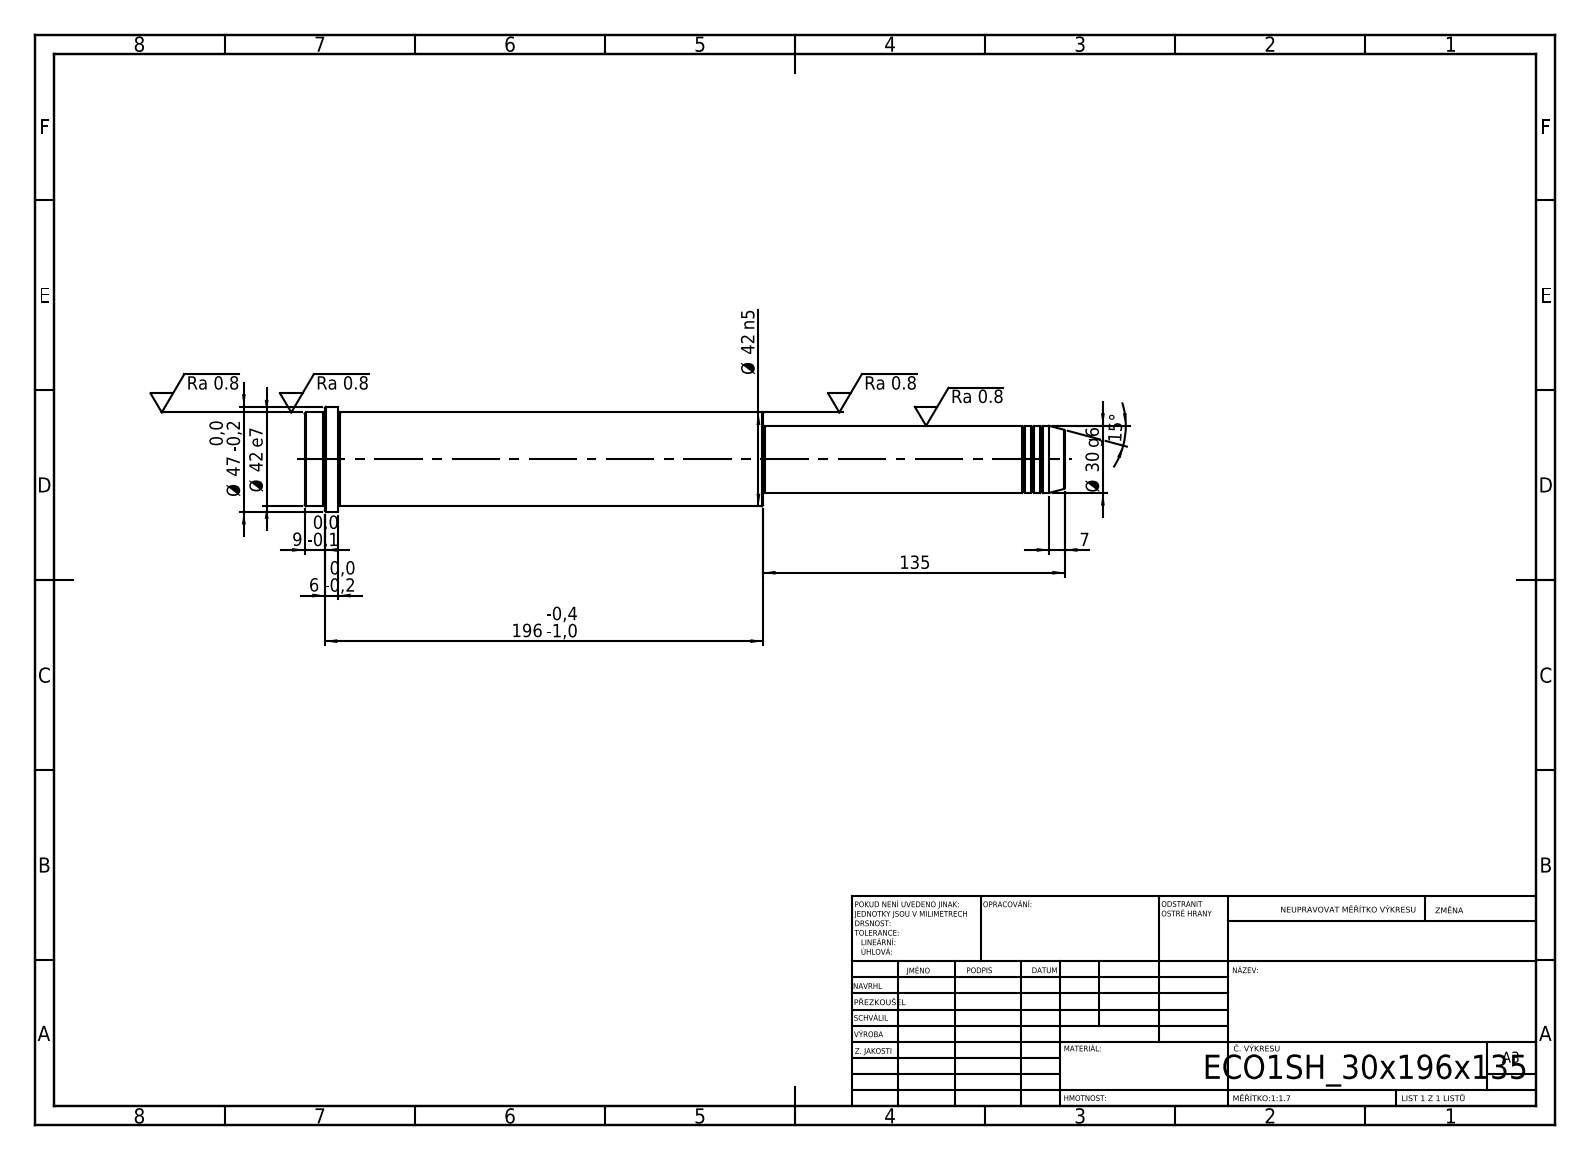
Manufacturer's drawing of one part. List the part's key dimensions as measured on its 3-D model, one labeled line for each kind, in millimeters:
STEP written by: SolidWorks 2019 (CONFIG_CONTROL_DESIGN)
Units: millimetres
Bodies: 1 solid, 52 faces (6 planar, 16 cylindrical, 30 other)
Overall size (bounding box): 340 × 47 × 47
Volume: 380 634 mm³ · Surface area: 43 406 mm²
Round bosses / shafts (diameter × count): ⌀47 ×1, ⌀42 ×1, ⌀30 ×1, ⌀29 ×1
Main face-to-face distances: 205, 135, 340, 325, 190, 15, 331, 196, 6, 9
